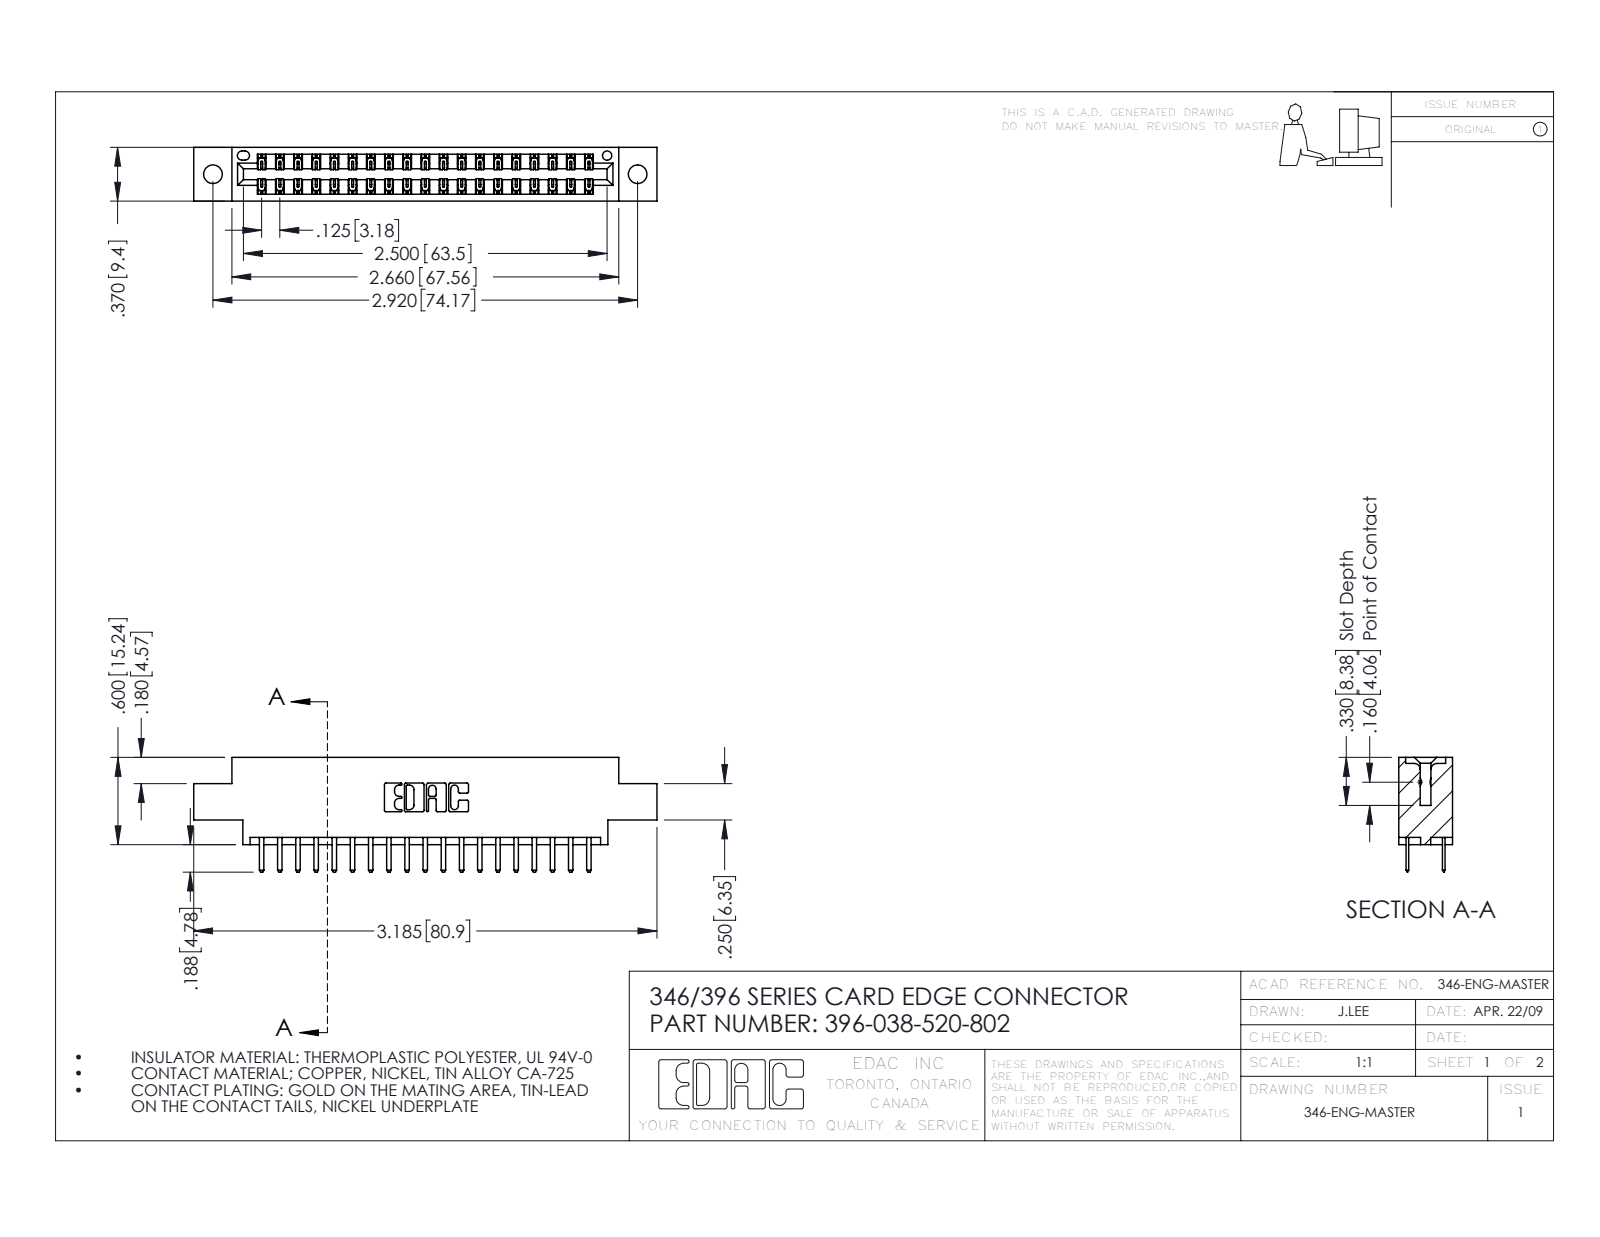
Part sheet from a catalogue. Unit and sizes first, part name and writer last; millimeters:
Units: millimetres
Overall size (bounding box): 80.9 × 20 × 9.4
Round holes (diameter × count): ⌀3.3 ×2, ⌀1.6 ×1
Partial cylindrical surfaces — rounded edges, fillets, slot ends (radius × count): R0.2 ×57, R0.3 ×42, R0.3 ×22, R0.2 ×6, R0.8 ×6, R0.7 ×3, R0.4 ×2, R0.6 ×2
Main face-to-face distances: 1.2, 8.2, 6.4, 9.4, 7, 1.8, 7.6, 0.6, 3.8, 5.6
Hole centre spacings: 6.2, 68.9, 74.2
Volume: 7 510 mm³ · Surface area: 9 819 mm²
Bodies: 39 solids, 2254 faces (1486 planar, 768 cylindrical, 0 other)
Part name (STEP PRODUCT): 396-038-520-802; 346 Part_0.170 Offset - 0.128 Dia; 345-292-001_345-293-120
STEP written by: SolidWorks 2016 (CONFIG_CONTROL_DESIGN)
